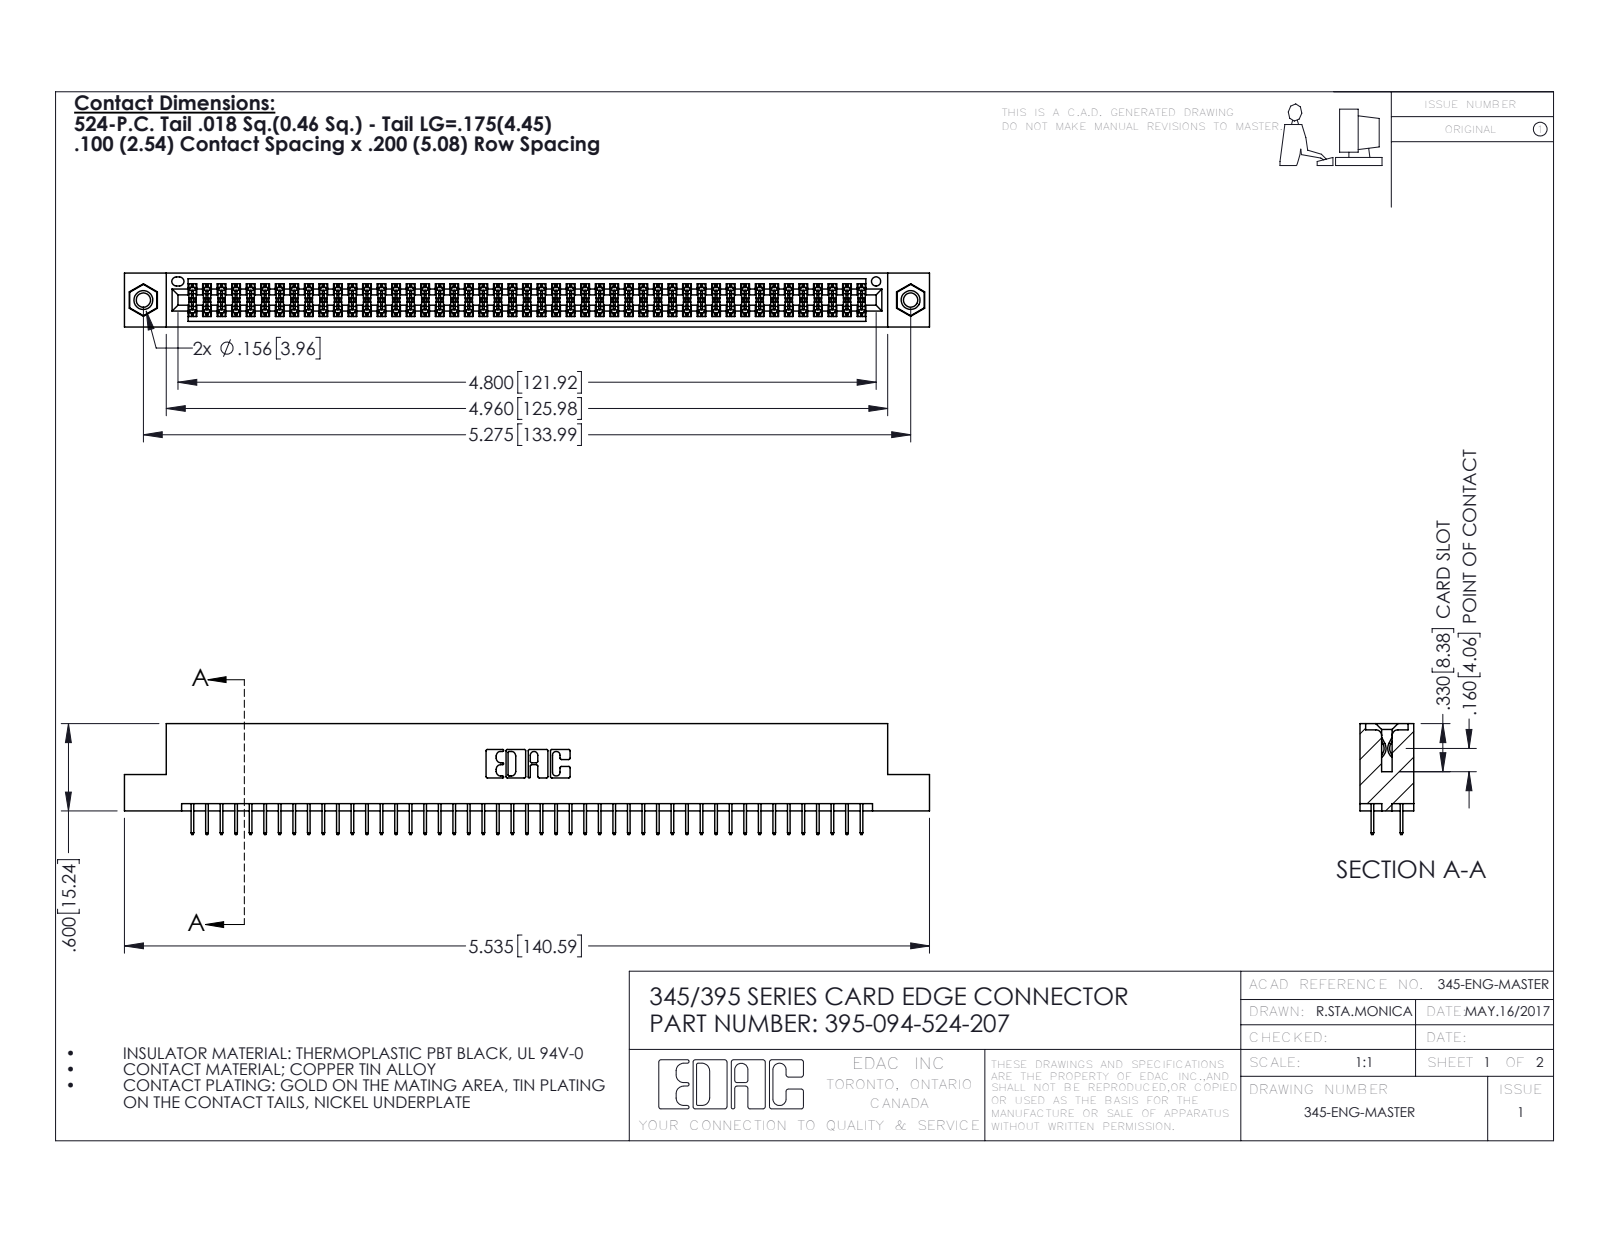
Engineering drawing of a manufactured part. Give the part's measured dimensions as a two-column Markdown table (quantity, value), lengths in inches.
| quantity | value |
| --- | --- |
| part name | 395-094-524-207; 345 Part_Flush Mounting Lugs - 0.156 Dia-TI; 345-250-001_345-250-005-103; 345-292-001_345-293-124 |
| STEP written by | SolidWorks 2016 (CONFIG_CONTROL_DESIGN) |
| units | inches |
| bodies | 97 solids, 5262 faces (3778 planar, 1468 cylindrical, 16 other) |
| overall size | 5.535 × 0.762 × 0.37 |
| volume | 0.827 in³ |
| surface area | 30.65 in² |
| round holes (diameter × count) | 0.098 × 2, 0.125 × 2, 0.156 × 2, 0.064 × 1 |
| round bosses / shafts (diameter × count) | 0.155 × 2 |
| partial cylindrical surfaces (radius × count) | 0.006 × 141, 0.01 × 22, 0.007 × 6, 0.031 × 6, 0.026 × 3, 0.014 × 2, 0.019 × 2, 0.022 × 2 |
| main face-to-face distances | 0.072, 0.298, 0.2, 0.37, 0.098, 0.272, 0.025, 0.225, 0.072, 0.175 |
| hole center spacings | 0.27, 5.039, 5.275 |
